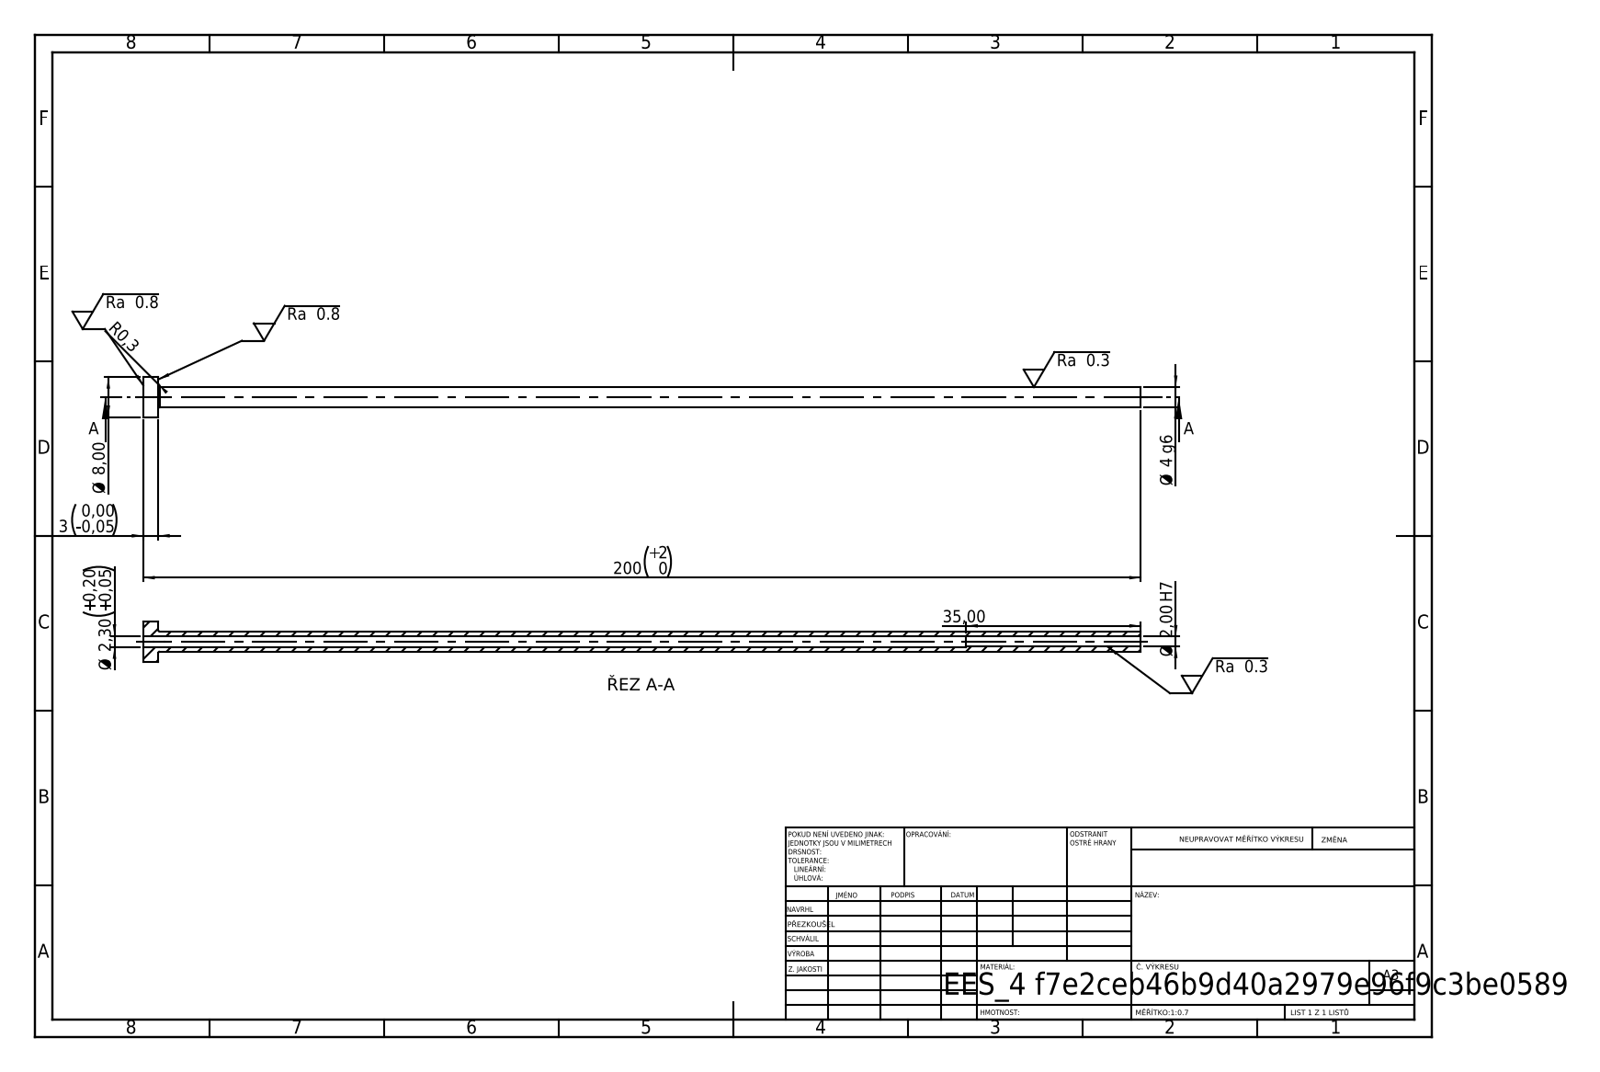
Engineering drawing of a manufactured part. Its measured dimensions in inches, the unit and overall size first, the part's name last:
Units: inches
Overall size (bounding box): 7.874 × 0.315 × 0.315
Round holes (diameter × count): ⌀0.079 ×1, ⌀0.091 ×1
Round bosses / shafts (diameter × count): ⌀0.315 ×1, ⌀0.157 ×1
Main face-to-face distances: 0.118, 7.874, 7.756, 6.496, 6.378, 1.378
Volume: 0.112 in³ · Surface area: 6.287 in²
Bodies: 1 solid, 14 faces (4 planar, 8 cylindrical, 2 other)
STEP written by: SolidWorks 2019 (CONFIG_CONTROL_DESIGN)
